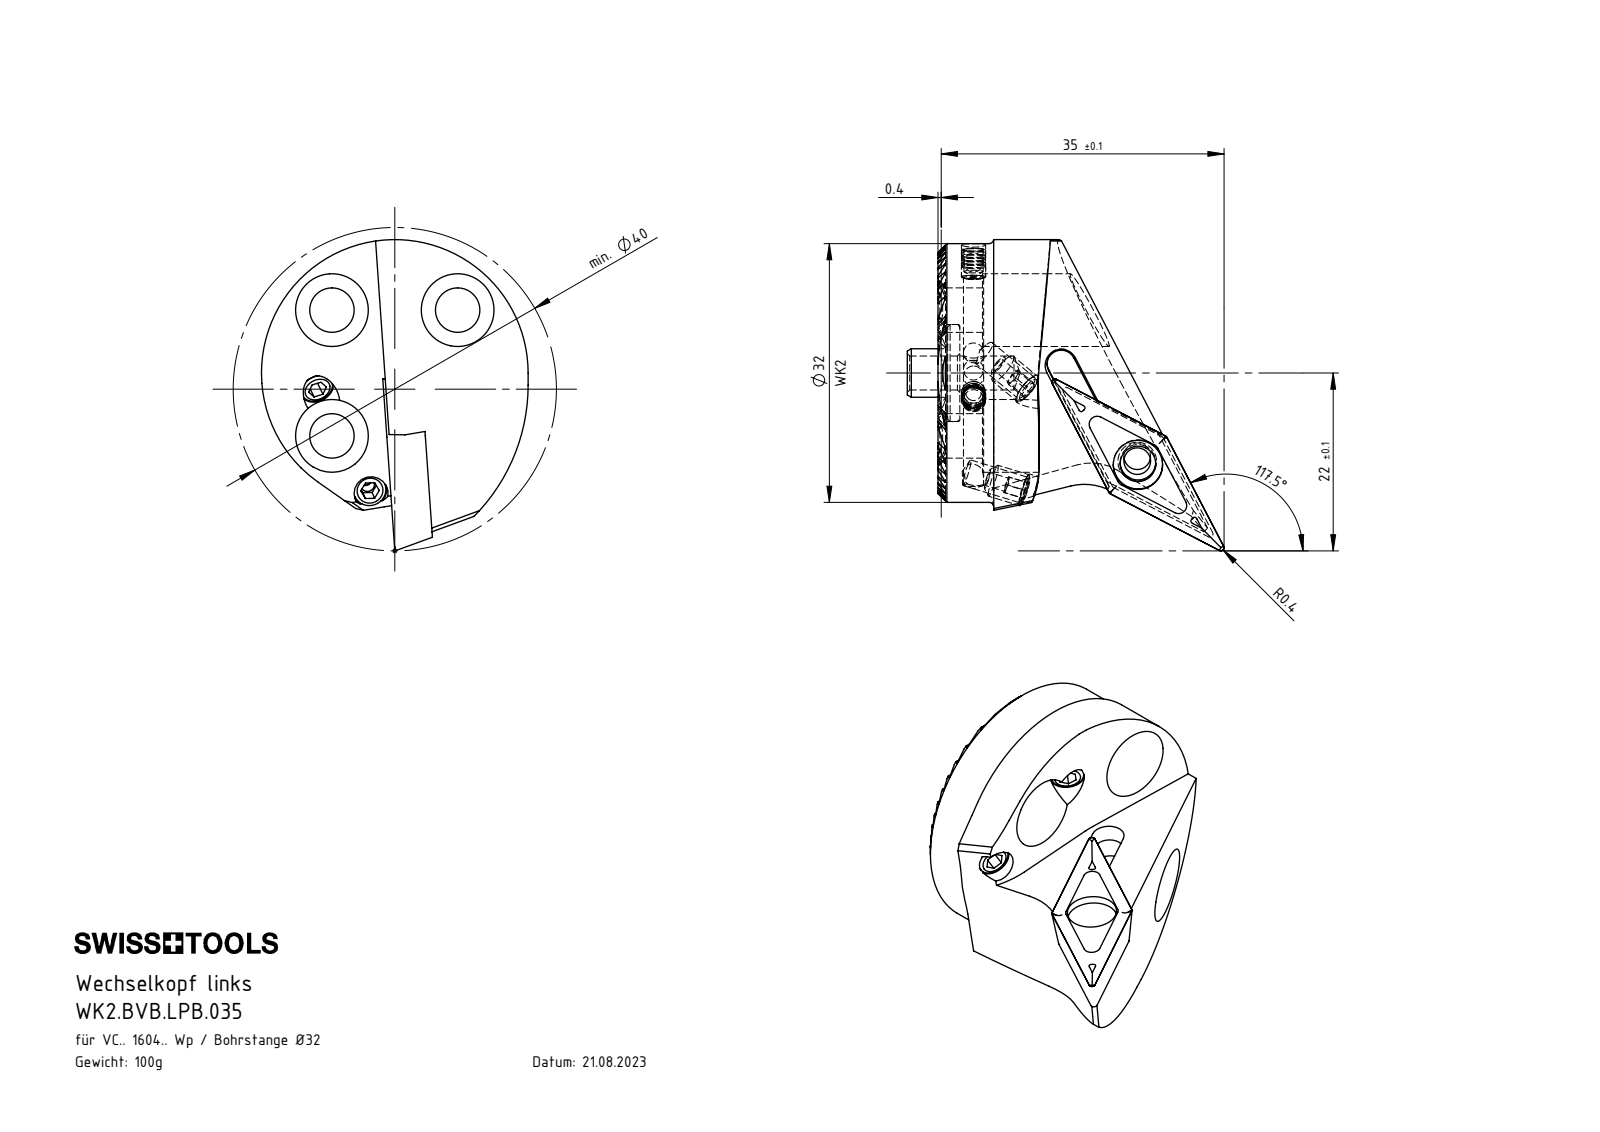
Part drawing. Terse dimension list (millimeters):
name: KVT_MB_600_030; WK2-BVB.LPB.035_A; VCMT160404; WKX-ER1.004.005_A_PreviewCfg (+2 more)
written by: SolidWorks 2017 (AUTOMOTIVE_DESIGN)
unit: mm
bodies: 9 solids, 357 faces (193 planar, 83 cylindrical, 81 other)
size: 39.2 × 38.5 × 33
volume: 12 339 mm³; area: 7 490 mm²
holes: 3× ⌀3.3, 3× ⌀4.2, 3× ⌀5.5, 3× ⌀9, 2× ⌀1.7, 2× ⌀2.38, 2× ⌀2.5, 2× ⌀3, 1× ⌀4.4, 1× ⌀6.1, 1× ⌀12
bosses: 2× ⌀4, 2× ⌀3, 1× ⌀32, 1× ⌀6
rounds: 22× R0.12, 2× R12, 1× R1.75, 1× R7, 1× R16.5, 1× R23
face distances: 1.3, 2.6, 3.9, 5.2, 6.5, 12.99, 11.69, 14.29, 7.8, 10.39
hole spacings: 11, 15.56, 22.01
